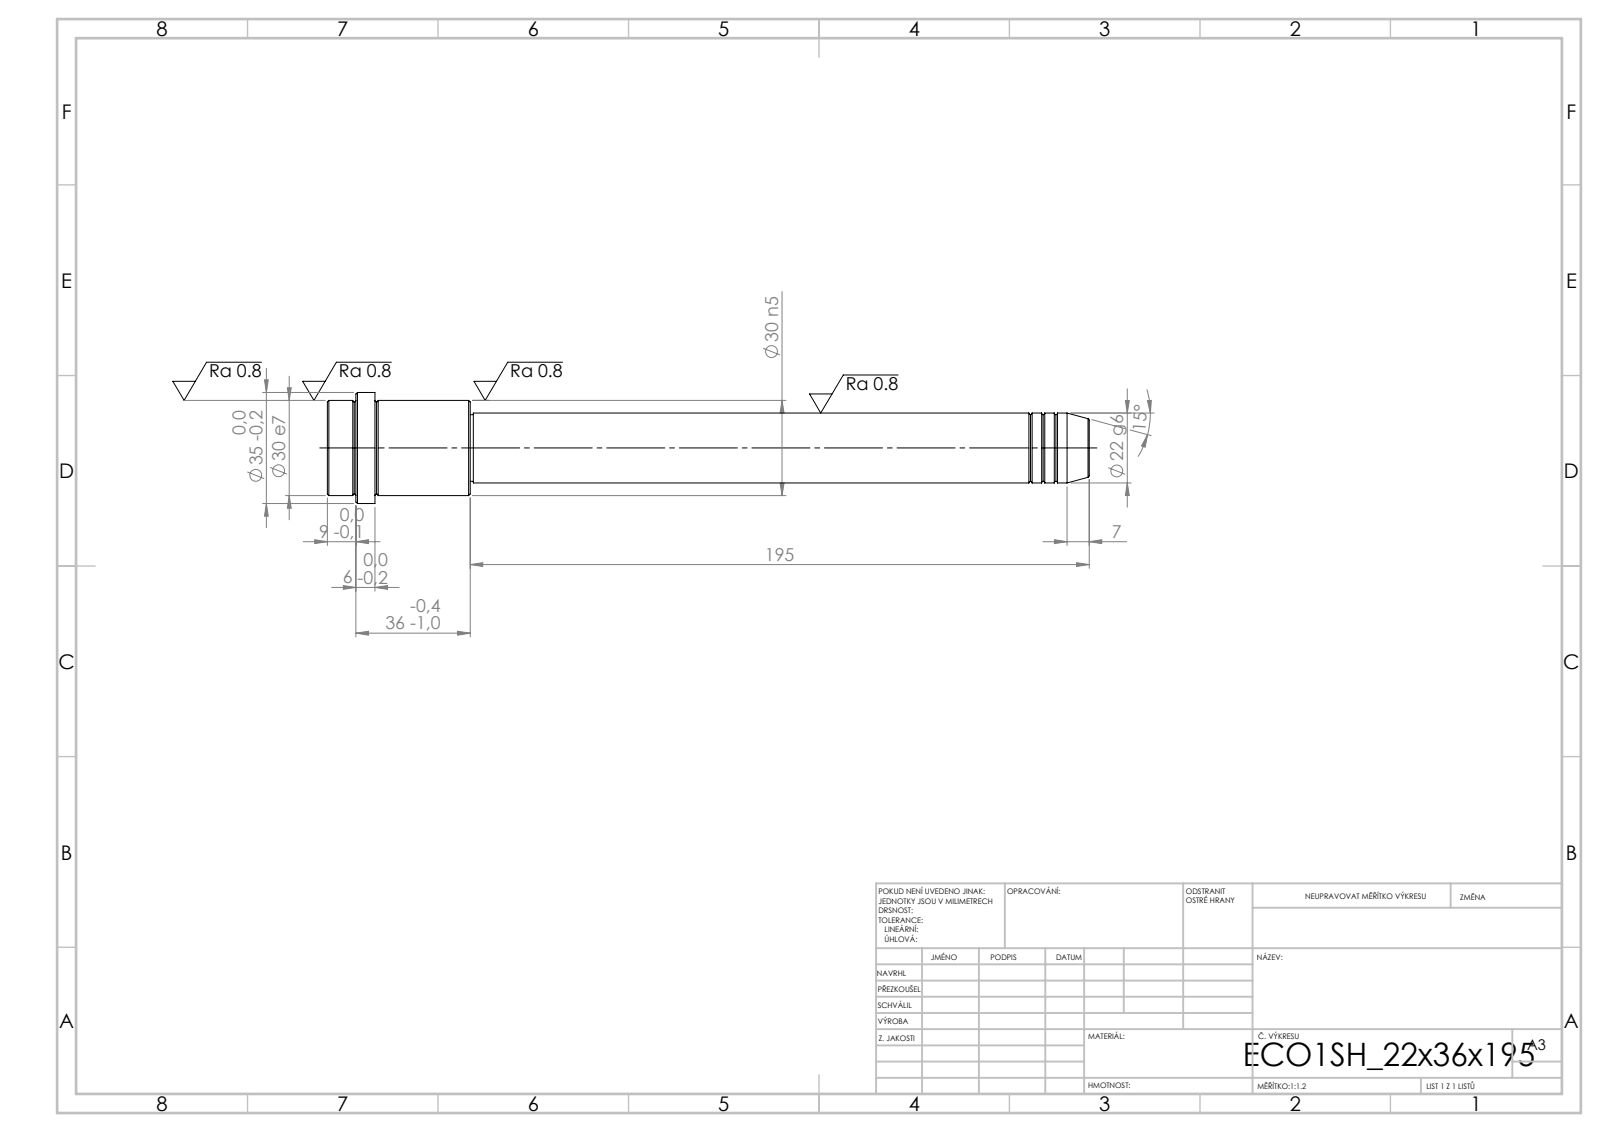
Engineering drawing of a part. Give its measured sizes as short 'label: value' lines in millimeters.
written by: SolidWorks 2019 (CONFIG_CONTROL_DESIGN)
unit: mm
bodies: 1 solid, 52 faces (6 planar, 16 cylindrical, 30 other)
size: 240 × 35 × 35
volume: 106 813 mm³; area: 19 773 mm²
bosses: 1× ⌀35, 1× ⌀30, 1× ⌀22, 1× ⌀21
face distances: 45, 30, 15, 195, 225, 240, 231, 36, 6, 9
